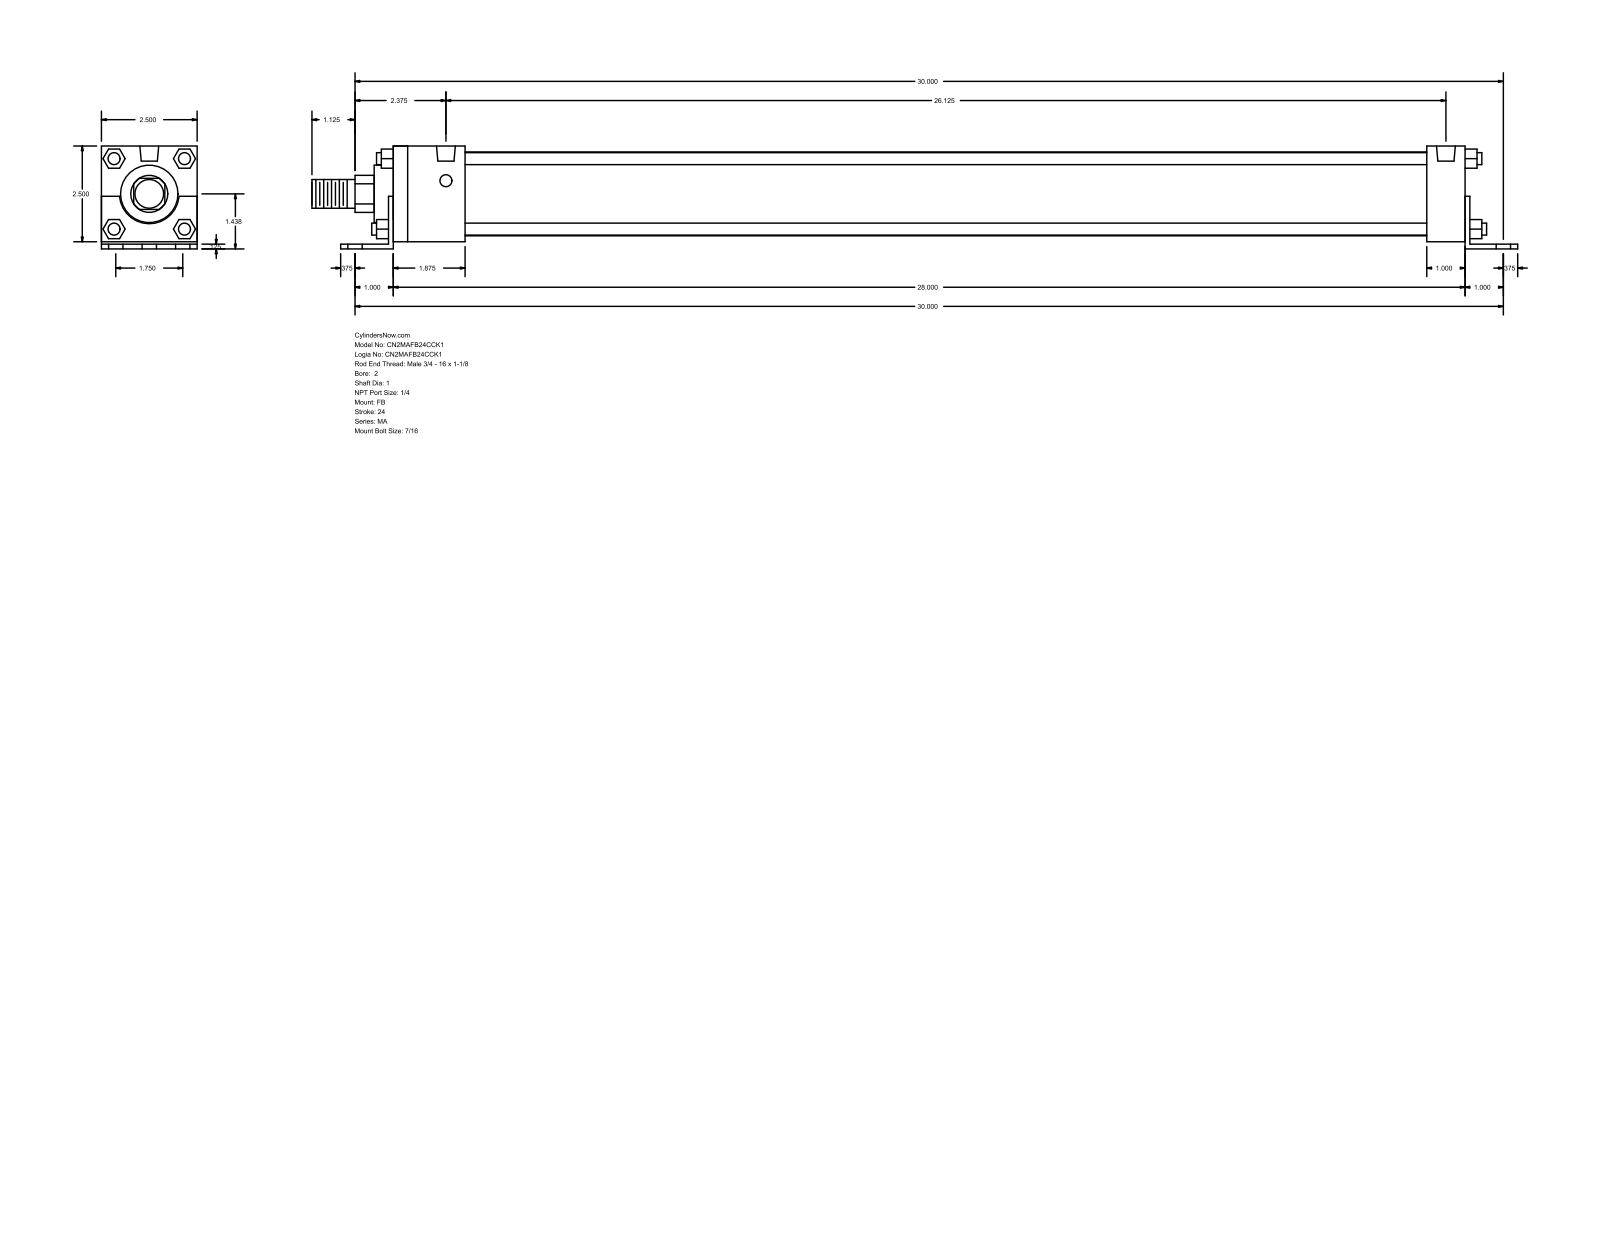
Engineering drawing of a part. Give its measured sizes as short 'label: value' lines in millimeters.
name: MA_FB__0200_1
written by: GSSL Pune (CONFIG_CONTROL_DESIGN)
unit: mm
bodies: 0 solids, 140 faces (105 planar, 35 cylindrical, 0 other)
size: 800.1 × 68.26 × 63.5
holes: 6× ⌀11.11, 4× ⌀7.94, 2× ⌀12.49
bosses: 4× ⌀7.94, 1× ⌀55.63, 1× ⌀38.1, 1× ⌀25.4, 1× ⌀19.05
rounds: 1× R12.29, 1× R19.81
face distances: 63.5, 3.17, 4.76, 68.26, 1.59, 65.09, 714.37, 12.7, 711.2, 28.57
hole spacings: 22.23, 762.32, 762, 44.11, 44.46, 64.3, 663.57, 702.02
